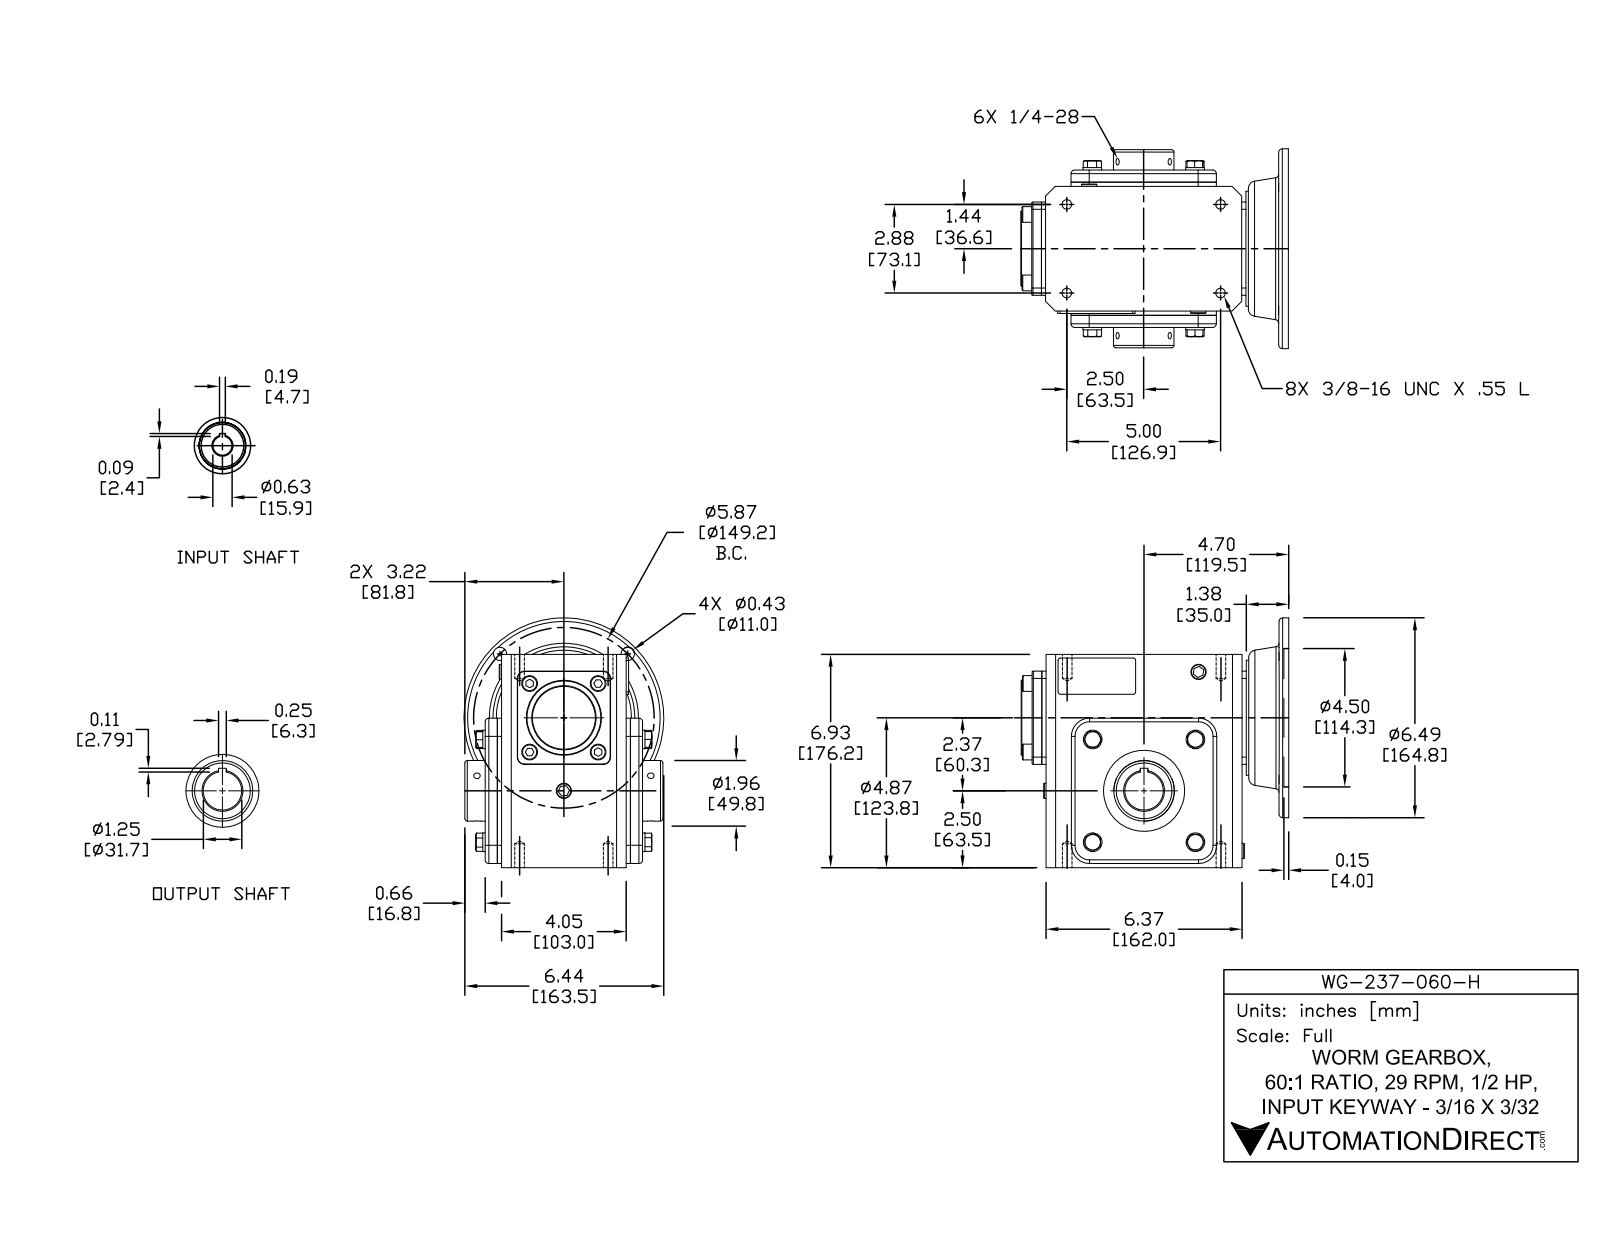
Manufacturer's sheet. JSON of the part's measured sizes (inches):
{"part_name": "WG-237-060-H", "step_written_by": "SolidWorks 2015 (CONFIG_CONTROL_DESIGN)", "units": "inches", "bodies": {"solids": 37, "faces": 609, "planar": 348, "cylindrical": 172, "other": 89}, "overall_size": [8.701, 8.123, 6.496], "volume_in3": 217.1, "surface_area_in2": 540.6, "round_holes": [[0.213, 6], [0.313, 4], [0.406, 4], [0.591, 1], [0.625, 1], [1.181, 1], [1.25, 1], [1.457, 1], [1.969, 1], [2.638, 1], [3.819, 1], [4.5, 1]], "round_bosses_or_shafts": [[0.606, 4], [0.512, 4], [6.496, 1], [3.74, 1], [2.441, 1], [2.047, 1], [1.142, 1]], "partial_cylinders_radius": [[0.079, 8], [0.118, 8], [0.236, 6], [0.591, 4], [0.02, 2], [0.039, 2]], "face_to_face_distances": [0.138, 4.331, 4.724, 0.531, 0.394, 4.193, 4.587, 6.516, 0.315, 6.937], "hole_center_spacings": [2.859, 2.937, 4.945, 5.653, 2.098, 2.88, 4.154, 4.154]}
